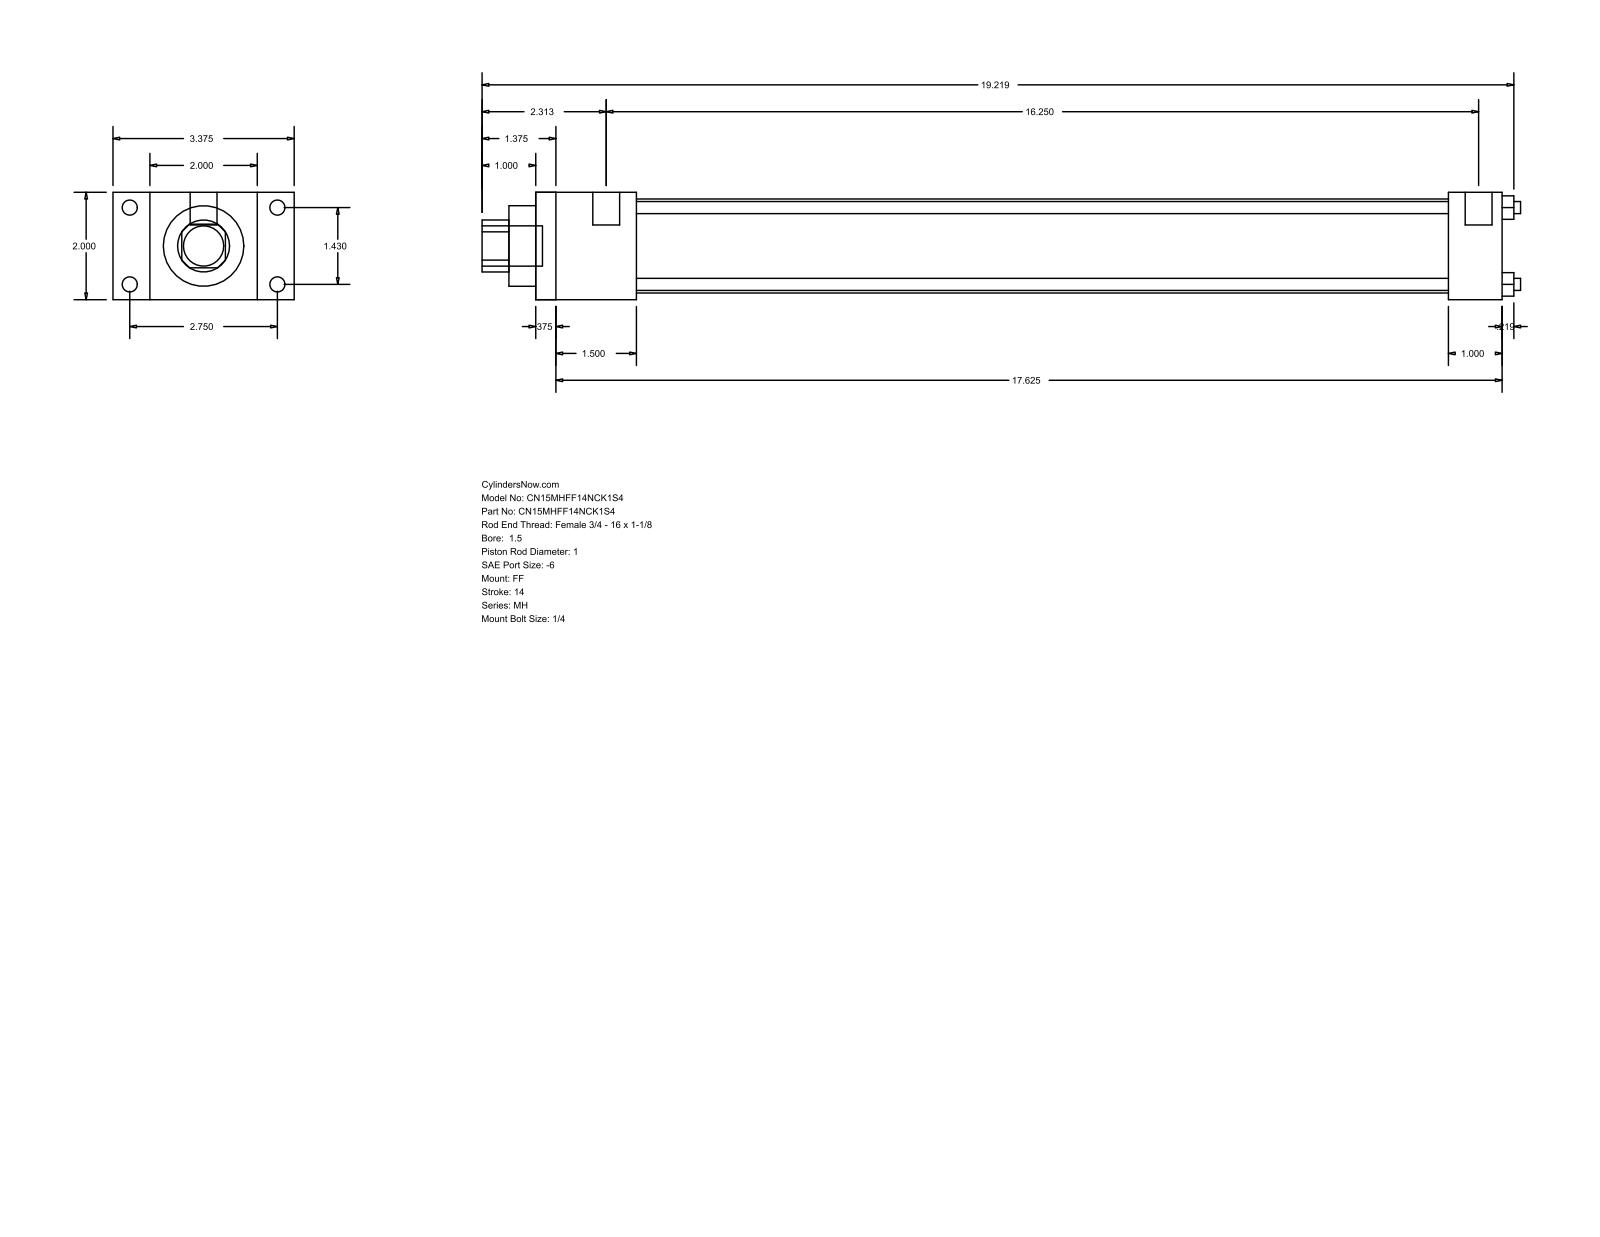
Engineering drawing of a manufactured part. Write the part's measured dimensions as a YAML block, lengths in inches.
part_name: "MH_FF__0150_1"
step_written_by: "GSSL Pune (CONFIG_CONTROL_DESIGN)"
units: inches
bodies: {solids: 0, faces: 92, planar: 64, cylindrical: 28, other: 0}
overall_size: [19.344, 3.375, 2]
round_holes:
  - {diameter: 0.225, count: 4}
  - {diameter: 1, count: 1}
  - {diameter: 1.5, count: 1}
  - {diameter: 1.75, count: 1}
round_bosses_or_shafts:
  - {diameter: 0.281, count: 4}
  - {diameter: 0.219, count: 4}
  - {diameter: 0.5, count: 2}
  - {diameter: 0.75, count: 1}
partial_cylinders:
  - {radius: 0.484, count: 1}
face_to_face_distances: [2, 18, 0.375, 17.625, 1, 0.687, 2.687, 1.875, 1.5, 16.125]
hole_center_spacings: [1.011, 1.43, 2.022]
